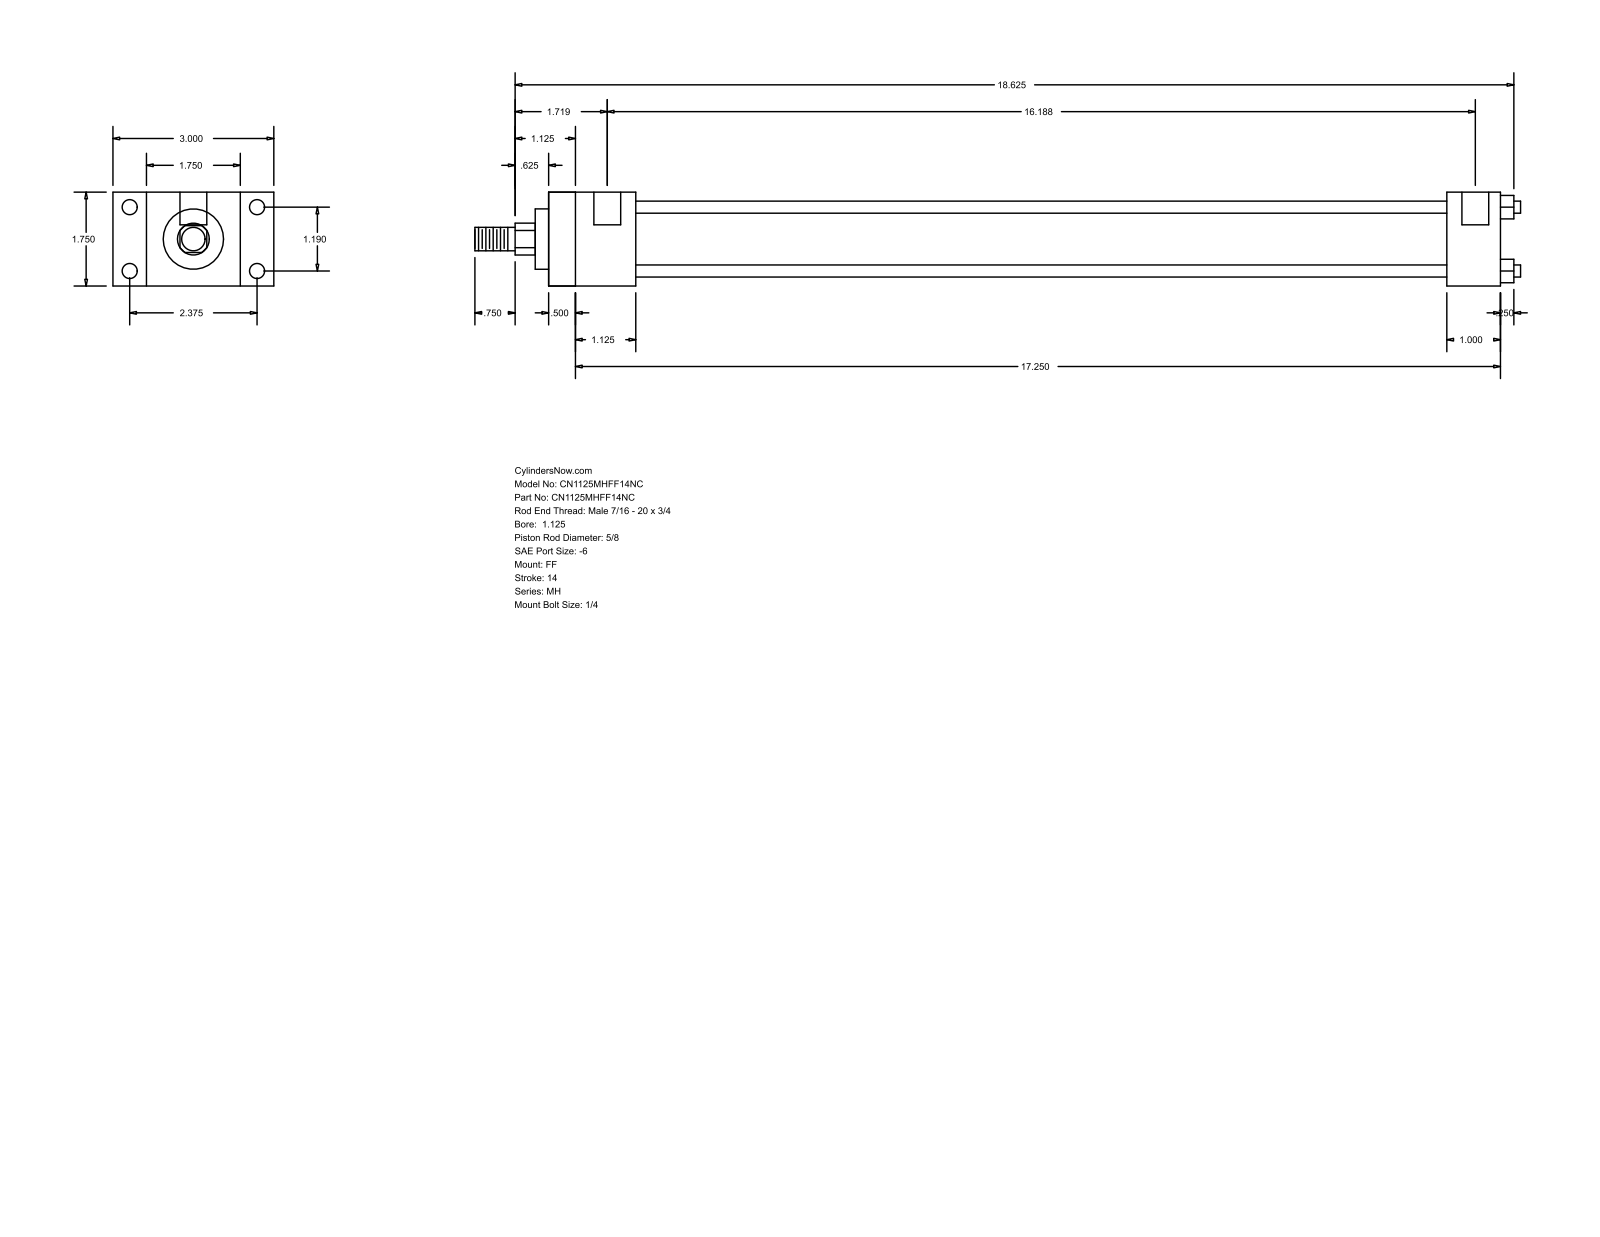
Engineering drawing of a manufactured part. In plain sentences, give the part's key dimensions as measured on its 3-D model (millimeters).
The part is named "MH_FF__0112_0.625". Its 3-D file was written by "GSSL Pune (CONFIG_CONTROL_DESIGN)". It is 0 solids with 92 faces: 64 planar, 28 cylindrical and 0 other. Overall it measures 495.3 by 76.2 by 44.45 millimeters. Round holes: 4 of diameter 5.56, 4 of diameter 7.14, 2 of diameter 12.7. Round bosses or shafts: 4 of diameter 5.71, 1 of diameter 34.92, 1 of diameter 28.57, 1 of diameter 15.88, 1 of diameter 11.11. Partial cylindrical surfaces (rounded edges, fillets, slot ends): 1 of radius 7.54. The main face-to-face distances are 44.46, 450.85, 15.87, 12.69, 438.16, 28.58, 60.33, 41.27, 425.44, 412.75. The hole center spacings are 30.22, 60.32, 67.47, 407.99, 3.17, 411.16.
